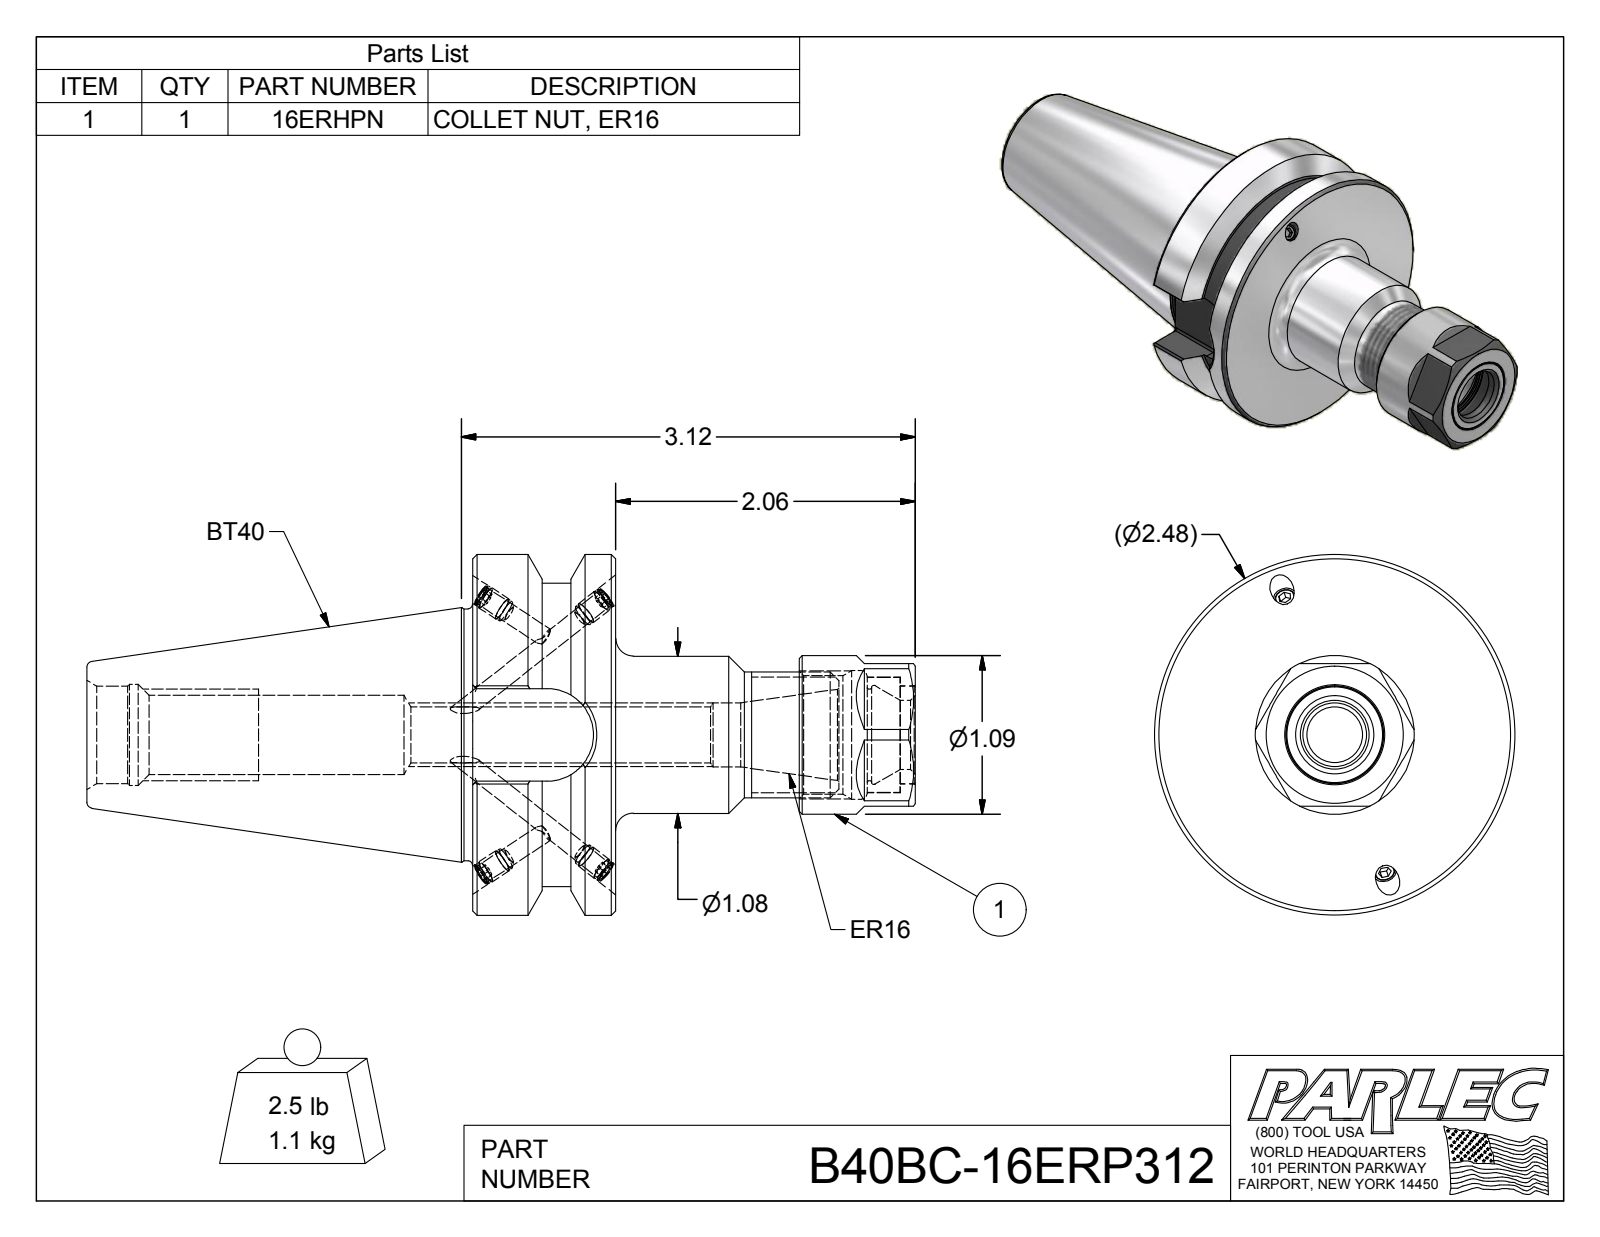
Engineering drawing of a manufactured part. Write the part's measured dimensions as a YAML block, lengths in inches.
part_name: "B40BC-16ERP312; B40BCB-16ER3-1; 029-965; 16ERHPN"
step_written_by: "Autodesk Inventor 2012 (AUTOMOTIVE_DESIGN)"
units: inches
bodies: {solids: 7, faces: 194, planar: 87, cylindrical: 53, other: 54}
overall_size: [5.695, 2.48, 2.48]
volume: 8.7
surface_area: 50.07
round_holes:
  - {diameter: 0.13, count: 4}
  - {diameter: 0.161, count: 4}
  - {diameter: 0.383, count: 1}
  - {diameter: 0.44, count: 1}
  - {diameter: 0.474, count: 1}
  - {diameter: 0.545, count: 1}
  - {diameter: 0.63, count: 1}
  - {diameter: 0.67, count: 1}
  - {diameter: 0.674, count: 1}
  - {diameter: 0.68, count: 1}
  - {diameter: 0.694, count: 1}
  - {diameter: 0.794, count: 1}
round_bosses_or_shafts:
  - {diameter: 0.165, count: 4}
  - {diameter: 0.157, count: 4}
  - {diameter: 2.48, count: 1}
  - {diameter: 2.087, count: 1}
  - {diameter: 1.73, count: 1}
  - {diameter: 1.092, count: 1}
  - {diameter: 1.08, count: 1}
  - {diameter: 0.866, count: 1}
partial_cylinders:
  - {radius: 0.02, count: 8}
  - {radius: 0.319, count: 1}
face_to_face_distances: [0.984, 0.98, 1.78, 3.042, 2.058, 0.172, 0.809, 2.246, 1.262, 0.796]
